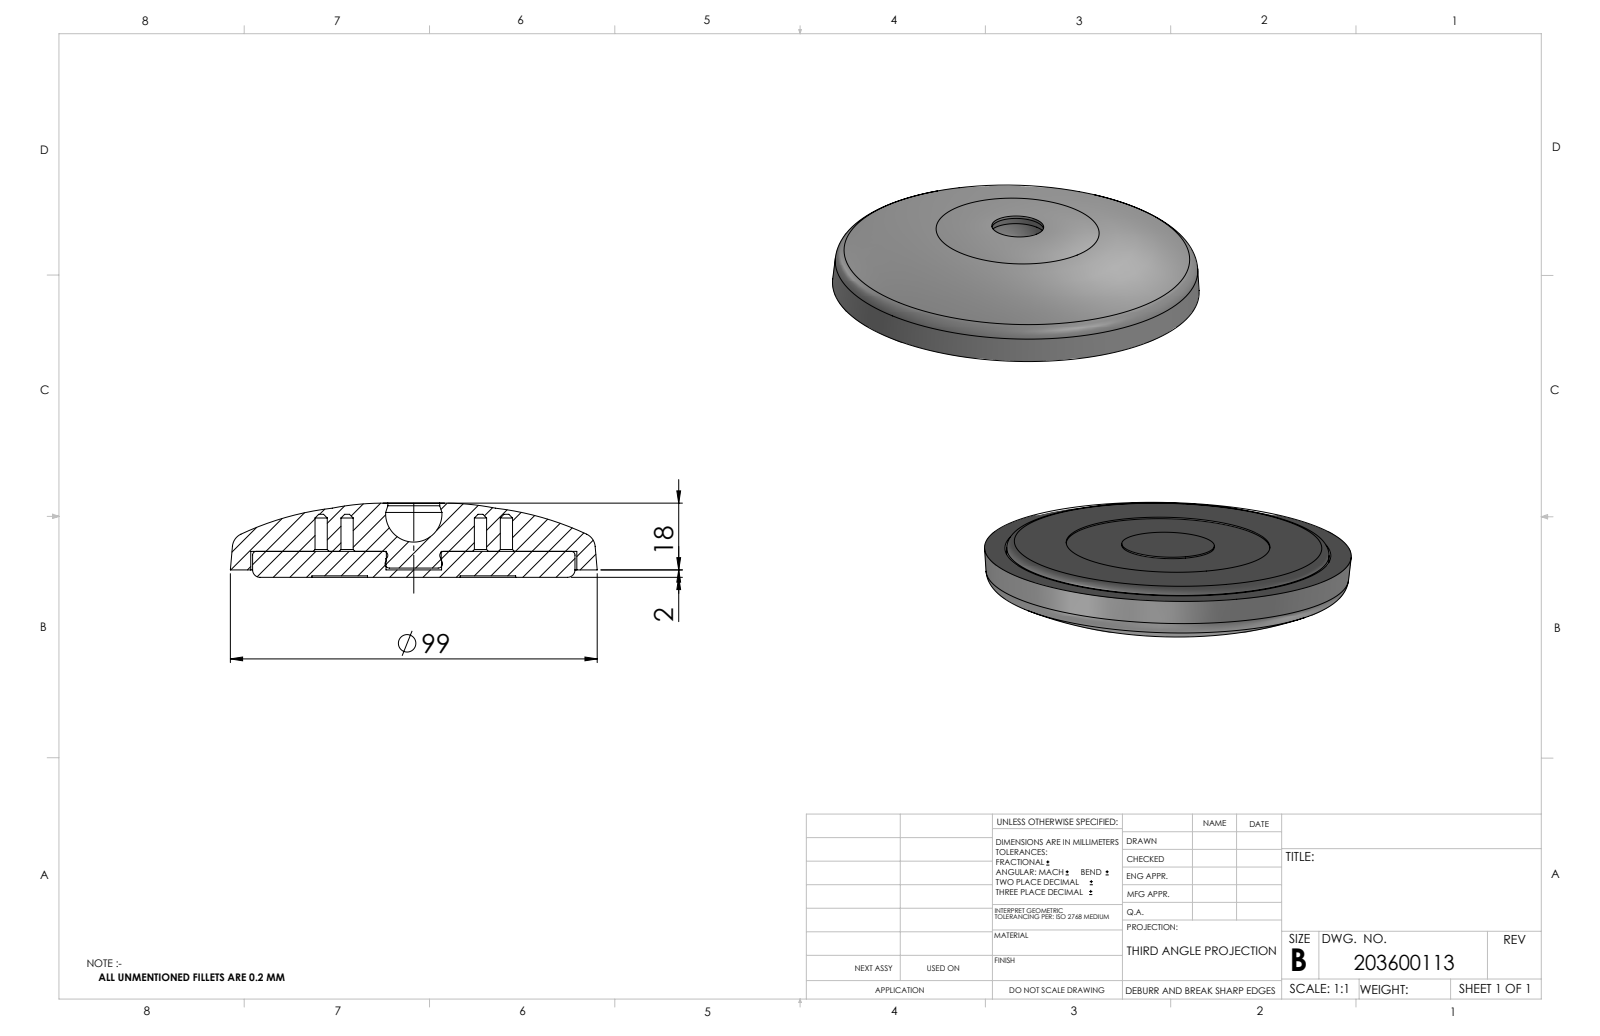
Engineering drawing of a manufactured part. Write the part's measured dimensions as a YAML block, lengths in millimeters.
part_name: "203600113_c_1"
step_written_by: "SolidWorks 2014 (CONFIG_CONTROL_DESIGN)"
units: millimeters
bodies: {solids: 2, faces: 307, planar: 66, cylindrical: 143, other: 98}
overall_size: [99, 99, 22.65]
volume: 91142
surface_area: 41820
round_holes:
  - {diameter: 3.3, count: 4}
  - {diameter: 9, count: 2}
  - {diameter: 14, count: 1}
  - {diameter: 15, count: 1}
  - {diameter: 55, count: 1}
  - {diameter: 88, count: 1}
round_bosses_or_shafts:
  - {diameter: 87, count: 1}
  - {diameter: 25, count: 1}
  - {diameter: 14.8, count: 1}
partial_cylinders:
  - {radius: 0.5, count: 51}
  - {radius: 3, count: 4}
  - {radius: 8, count: 2}
  - {radius: 15, count: 1}
  - {radius: 31, count: 1}
  - {radius: 34, count: 1}
face_to_face_distances: [7, 3, 0.4, 6.6, 2, 1.6, 5, 2.5, 2.1, 0.5]
hole_center_spacings: [41.15, 44.65, 7, 18, 25, 37, 43, 36]
